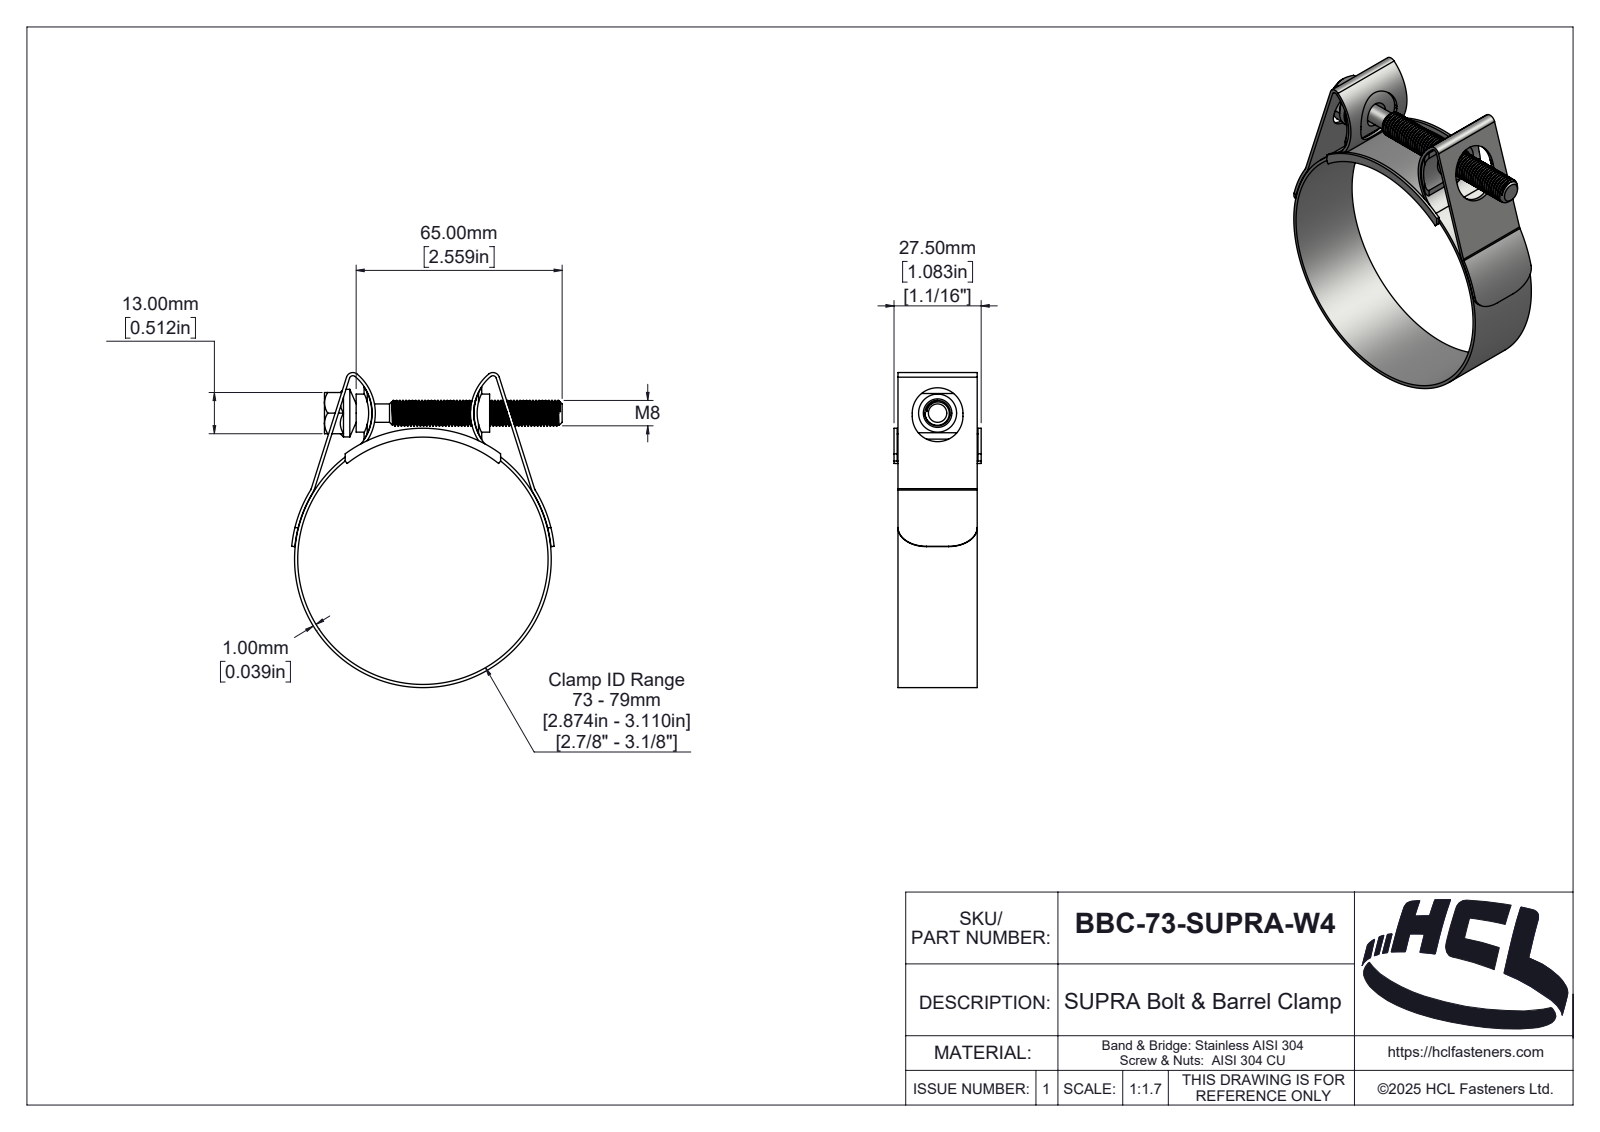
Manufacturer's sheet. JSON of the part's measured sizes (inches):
{"part_name": "BBC-73-SUPRA-W4", "step_written_by": "SolidWorks 2025 (AUTOMOTIVE_DESIGN)", "units": "inches", "bodies": {"solids": 5, "faces": 350, "planar": 46, "cylindrical": 218, "other": 86}, "overall_size": [3.912, 3.36, 1.083], "volume_in3": 0.935, "surface_area_in2": 41.06, "round_holes": [[3.11, 1]], "round_bosses_or_shafts": [[3.189, 1], [0.591, 1], [0.472, 1], [0.315, 1], [0.228, 1]], "partial_cylinders_radius": [[0.039, 4], [0.043, 2], [0.079, 2], [0.083, 2], [0.118, 2], [0.315, 2], [0.55, 2], [0.59, 2]], "face_to_face_distances": [0.039, 0.984, 0.049, 1.033, 1.043, 0.994, 1.083, 0.512, 0.098, 1.56]}
